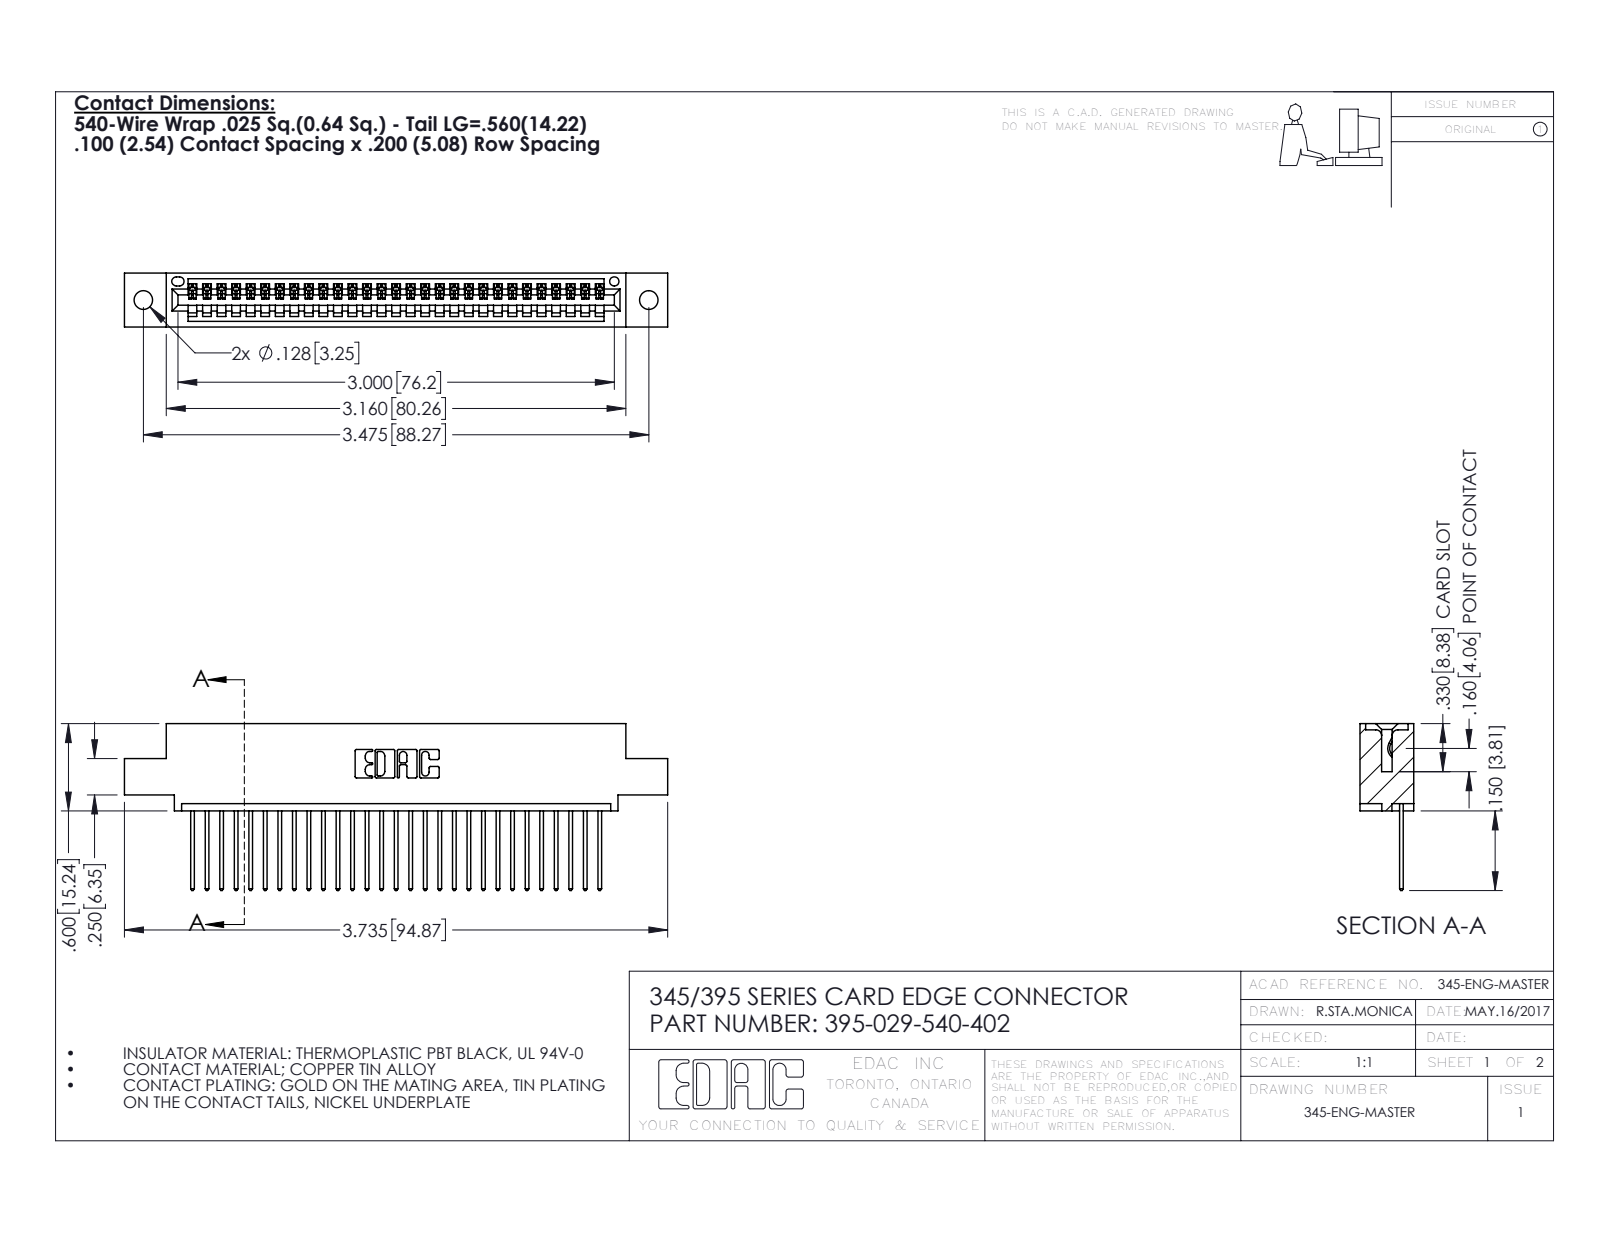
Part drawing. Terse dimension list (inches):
name: 395-029-540-402; 345 Part_0.110 Offset - 0.128 Dia; 345-292-001_345-293-140
written by: SolidWorks 2016 (CONFIG_CONTROL_DESIGN)
unit: in
bodies: 30 solids, 1812 faces (1244 planar, 568 cylindrical, 0 other)
size: 3.735 × 1.147 × 0.37
volume: 0.539 in³; area: 18.07 in²
holes: 2× ⌀0.128, 1× ⌀0.064
rounds: 58× R0.006, 58× R0.01, 22× R0.01, 6× R0.007, 6× R0.031, 3× R0.026, 2× R0.031, 2× R0.04
face distances: 0.298, 0.072, 0.37, 0.2, 0.098, 0.272, 0.025, 0.225, 0.149, 0.072
hole spacings: 0.27, 3.24, 3.475
